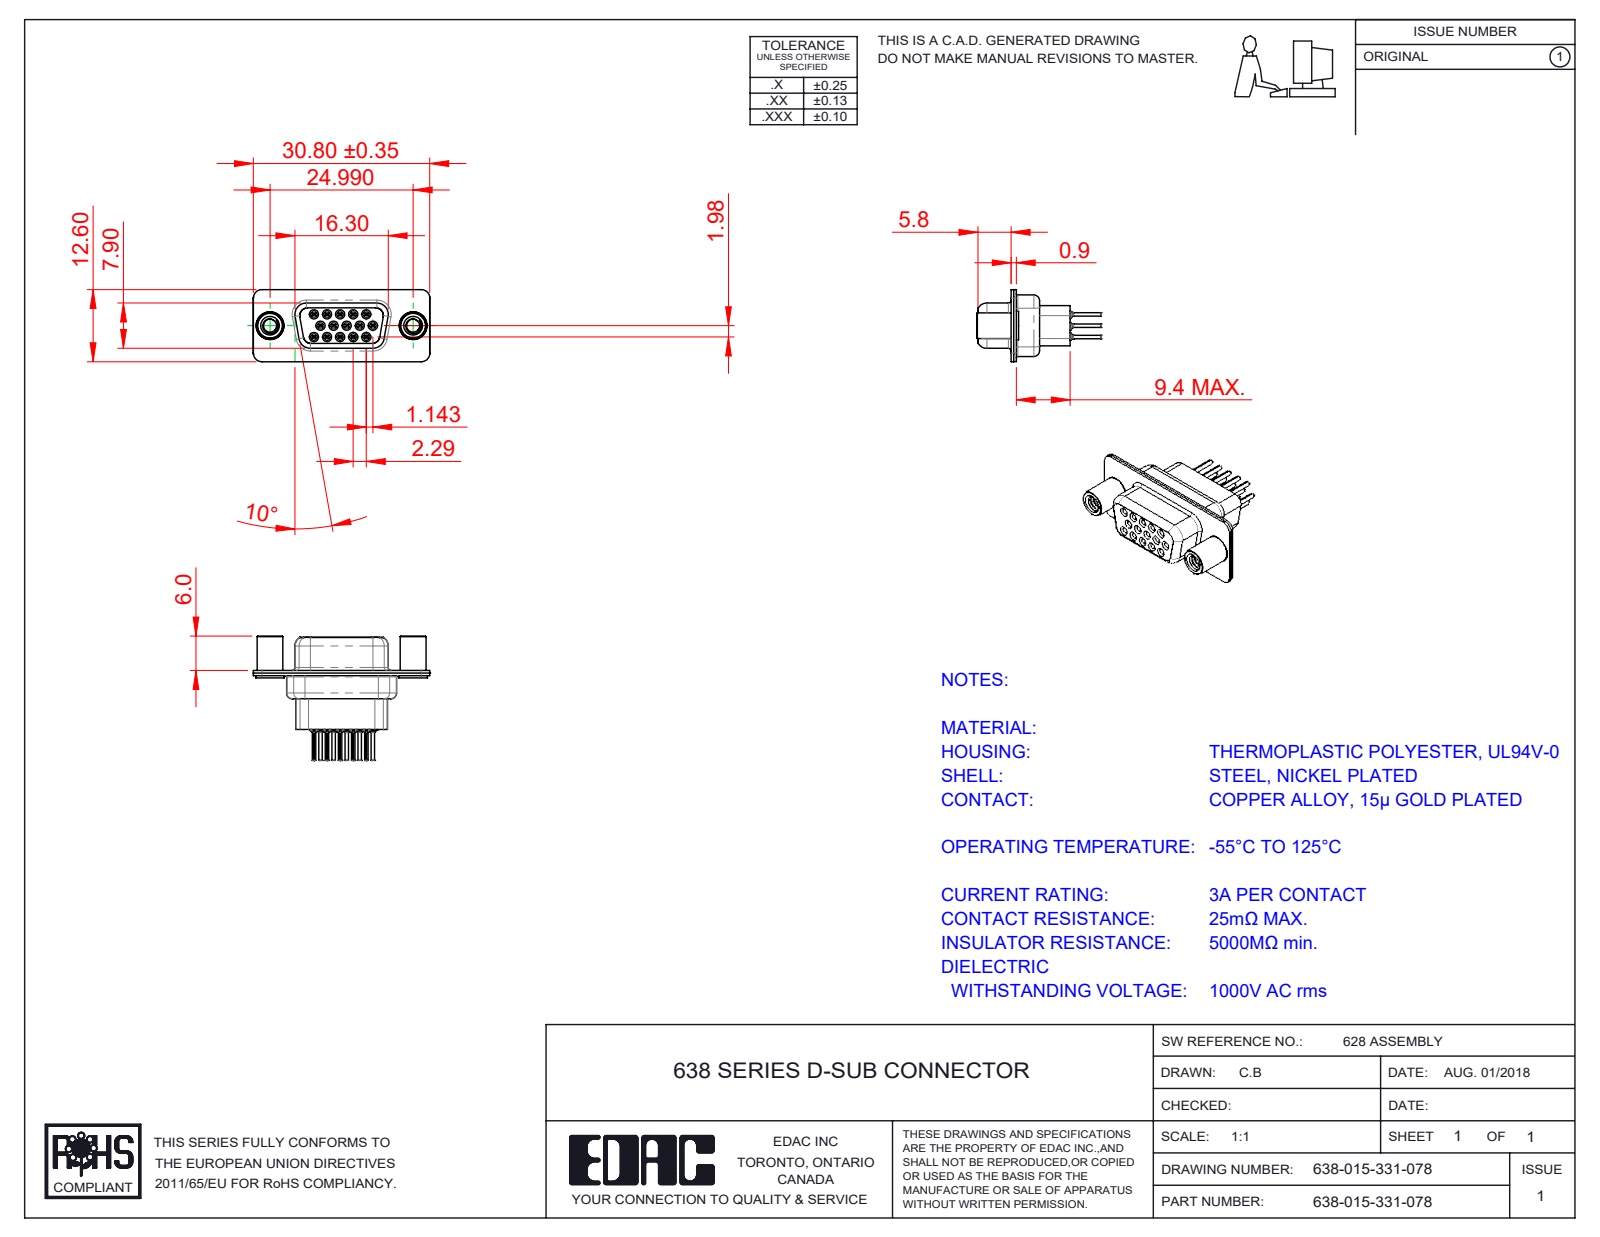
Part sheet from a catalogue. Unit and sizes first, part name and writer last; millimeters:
Units: millimetres
Overall size (bounding box): 30.81 × 21.7 × 12.6
Round holes (diameter × count): ⌀0.2 ×15, ⌀0.8 ×15, ⌀1 ×15, ⌀1.1 ×15, ⌀1.6 ×15, ⌀1.7 ×15, ⌀1.8 ×15, ⌀2 ×2, ⌀2.26 ×2, ⌀4 ×2, ⌀4.05 ×2, ⌀4.85 ×2
Round bosses / shafts (diameter × count): ⌀2 ×15, ⌀1.5 ×15, ⌀1.2 ×15, ⌀0.6 ×15, ⌀5 ×2, ⌀4.95 ×2, ⌀4.8 ×2, ⌀4.5 ×2
Partial cylindrical surfaces — rounded edges, fillets, slot ends (radius × count): R0.1 ×30, R1.5 ×20, R2 ×12, R0.28 ×10, R1.55 ×8, R1.35 ×5, R0.25 ×4, R0.5 ×4
Main face-to-face distances: 0.45, 0.9, 0.4, 1.43, 8.88, 6.6, 7, 2.28, 0.85, 5.8
Hole centre spacings: 3.96, 2.28, 4.57, 2.29, 6.05, 6.04, 6.86, 7.92
Volume: 1 946 mm³ · Surface area: 6 724 mm²
Bodies: 20 solids, 2158 faces (534 planar, 660 cylindrical, 964 other)
Part name (STEP PRODUCT): 638 Contact Row 2_31; 638 Housing_15 Contacts HP; 638 Contact Row 1_31; 638 Shell Front_15 Contacts (+4 more)
STEP written by: SolidWorks 2020 (CONFIG_CONTROL_DESIGN)
